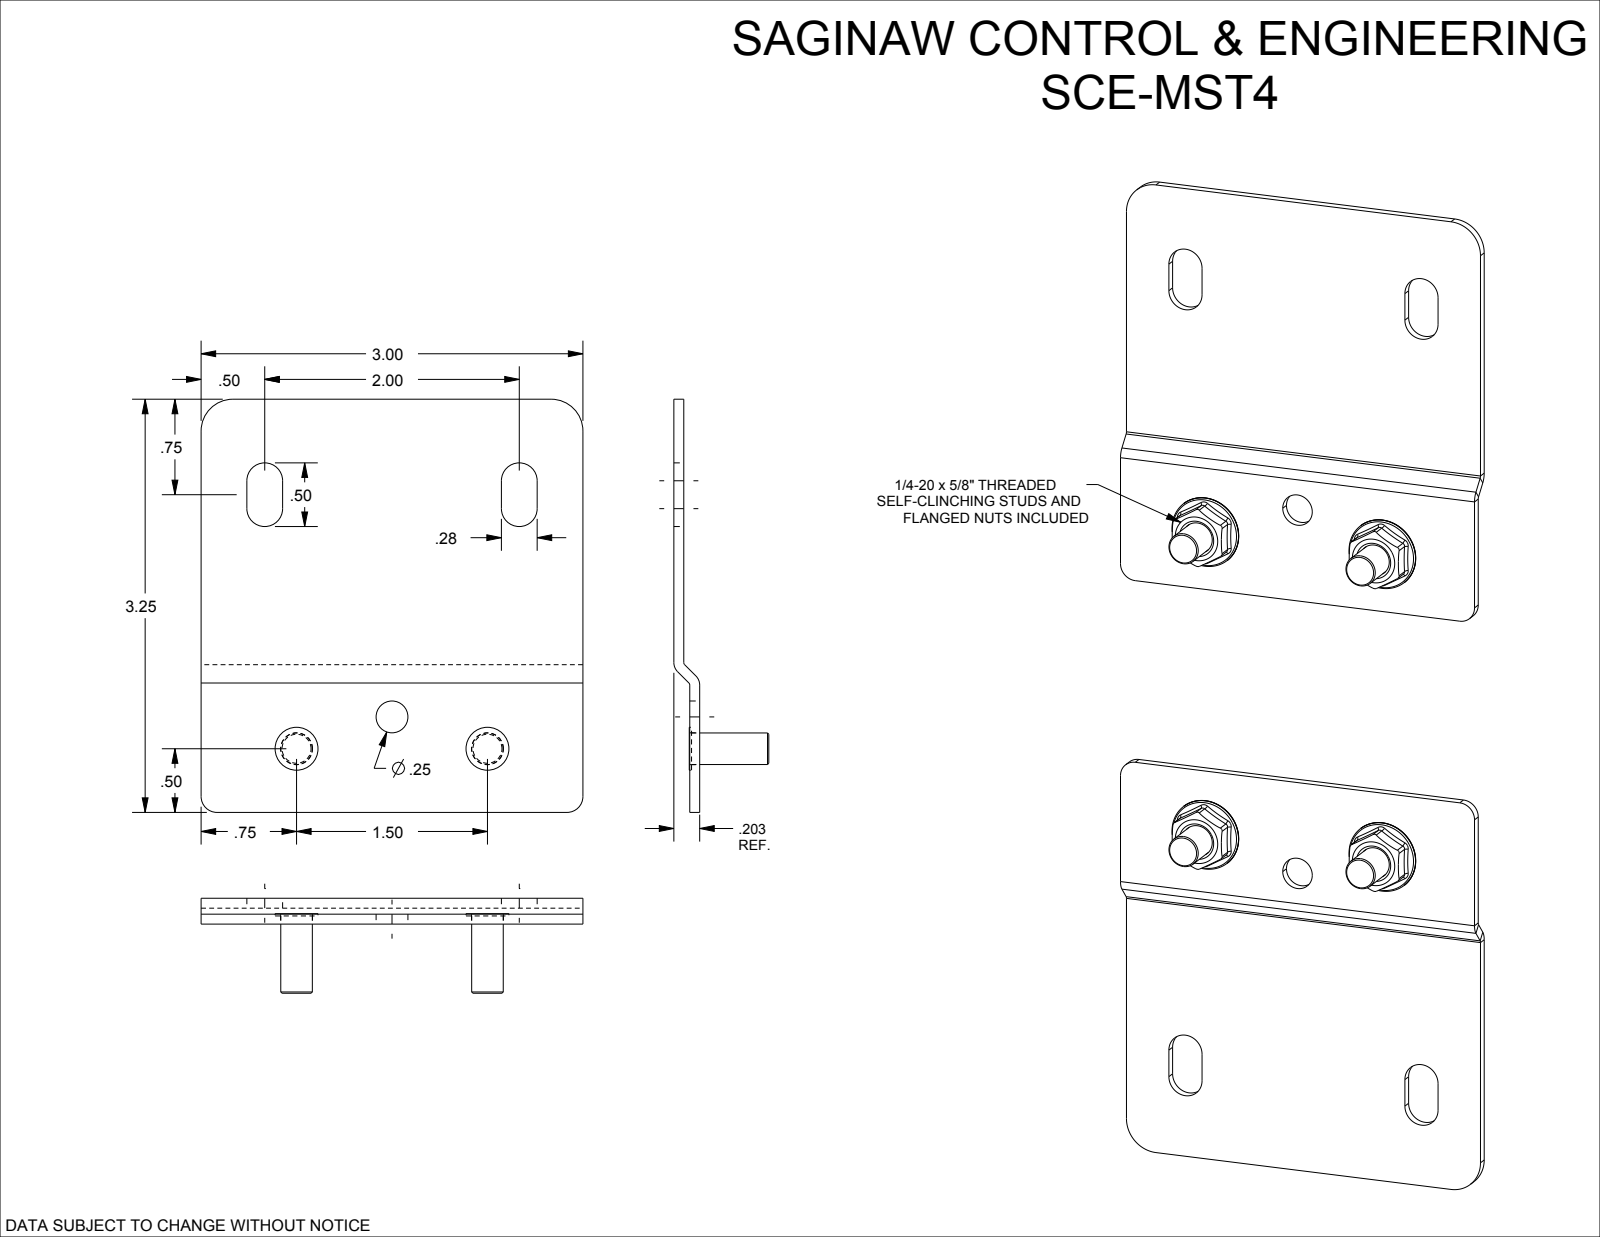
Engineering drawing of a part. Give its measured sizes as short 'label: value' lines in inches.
name: SCE-MST4
written by: SolidWorks 2019 (AUTOMOTIVE_DESIGN)
unit: in
bodies: 10 solids, 1010 faces (332 planar, 70 cylindrical, 608 other)
size: 7.99 × 3 × 0.746
volume: 1.681 in³; area: 46.1 in²
holes: 6× ⌀0.25, 4× ⌀0.25
bosses: 4× ⌀0.563, 4× ⌀0.337, 4× ⌀0.248
rounds: 24× R0.029, 8× R0.141, 4× R0.023, 4× R0.101, 4× R0.125, 4× R0.25
face distances: 0.078, 0.078, 0.125, 0.203, 0.047, 0.125, 3, 3.245, 4.745, 0.121
hole spacings: 0.791, 2.85, 1.5, 2.5, 2.915, 3
